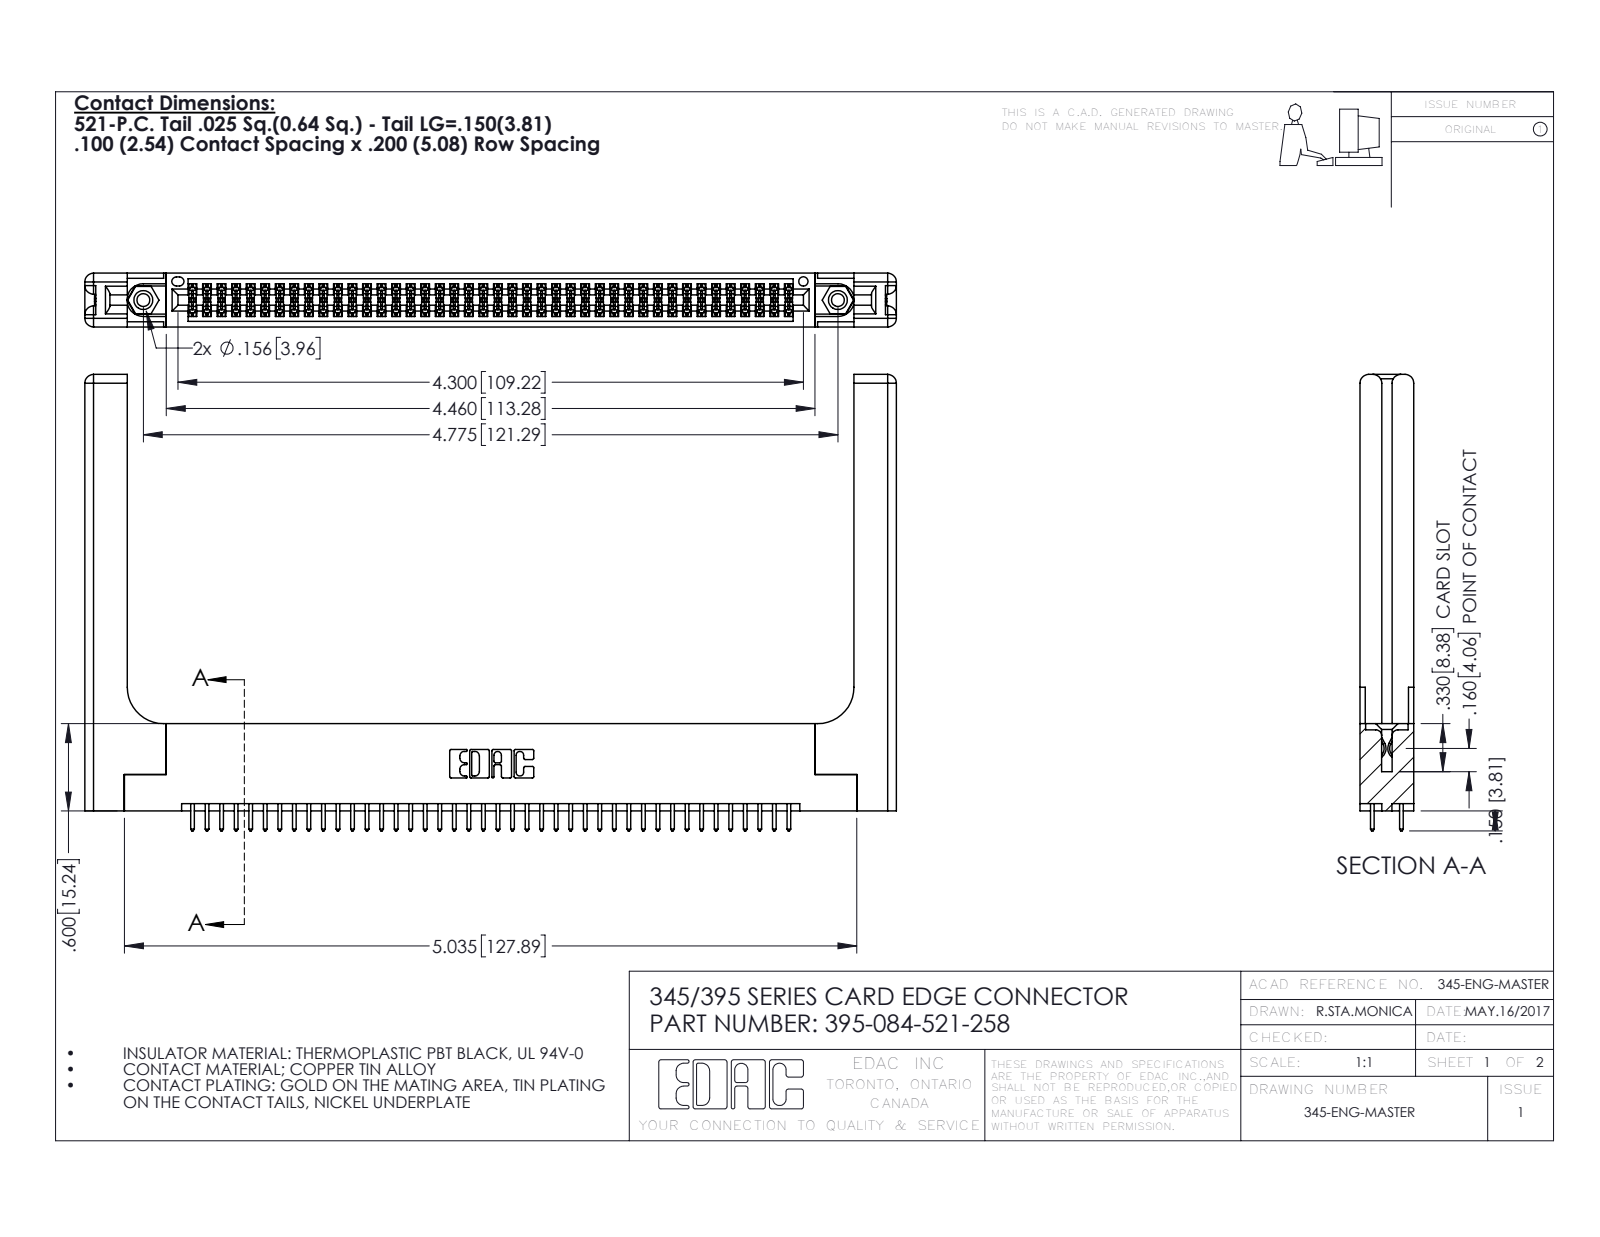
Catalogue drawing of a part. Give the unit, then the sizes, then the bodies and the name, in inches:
Units: inches
Overall size (bounding box): 5.579 × 3.137 × 0.37
Round holes (diameter × count): ⌀0.089 ×2, ⌀0.125 ×2, ⌀0.156 ×2, ⌀0.064 ×1
Round bosses / shafts (diameter × count): ⌀0.155 ×2
Partial cylindrical surfaces — rounded edges, fillets, slot ends (radius × count): R0.006 ×126, R0.01 ×84, R0.01 ×22, R0.06 ×16, R0.007 ×6, R0.031 ×6, R0.026 ×3, R0.014 ×2
Main face-to-face distances: 0.072, 0.298, 0.37, 0.2, 0.098, 0.272, 0.025, 0.225, 0.148, 0.15
Hole centre spacings: 0.27, 4.539, 4.775
Volume: 1.355 in³ · Surface area: 38.96 in²
Bodies: 89 solids, 4582 faces (3000 planar, 1522 cylindrical, 60 other)
Part name (STEP PRODUCT): 345-220-058_345-220-058; 345-250-001_345-250-001-102; 395-084-521-258; 345-292-001_345-293-121 (+1 more)
STEP written by: SolidWorks 2016 (CONFIG_CONTROL_DESIGN)
